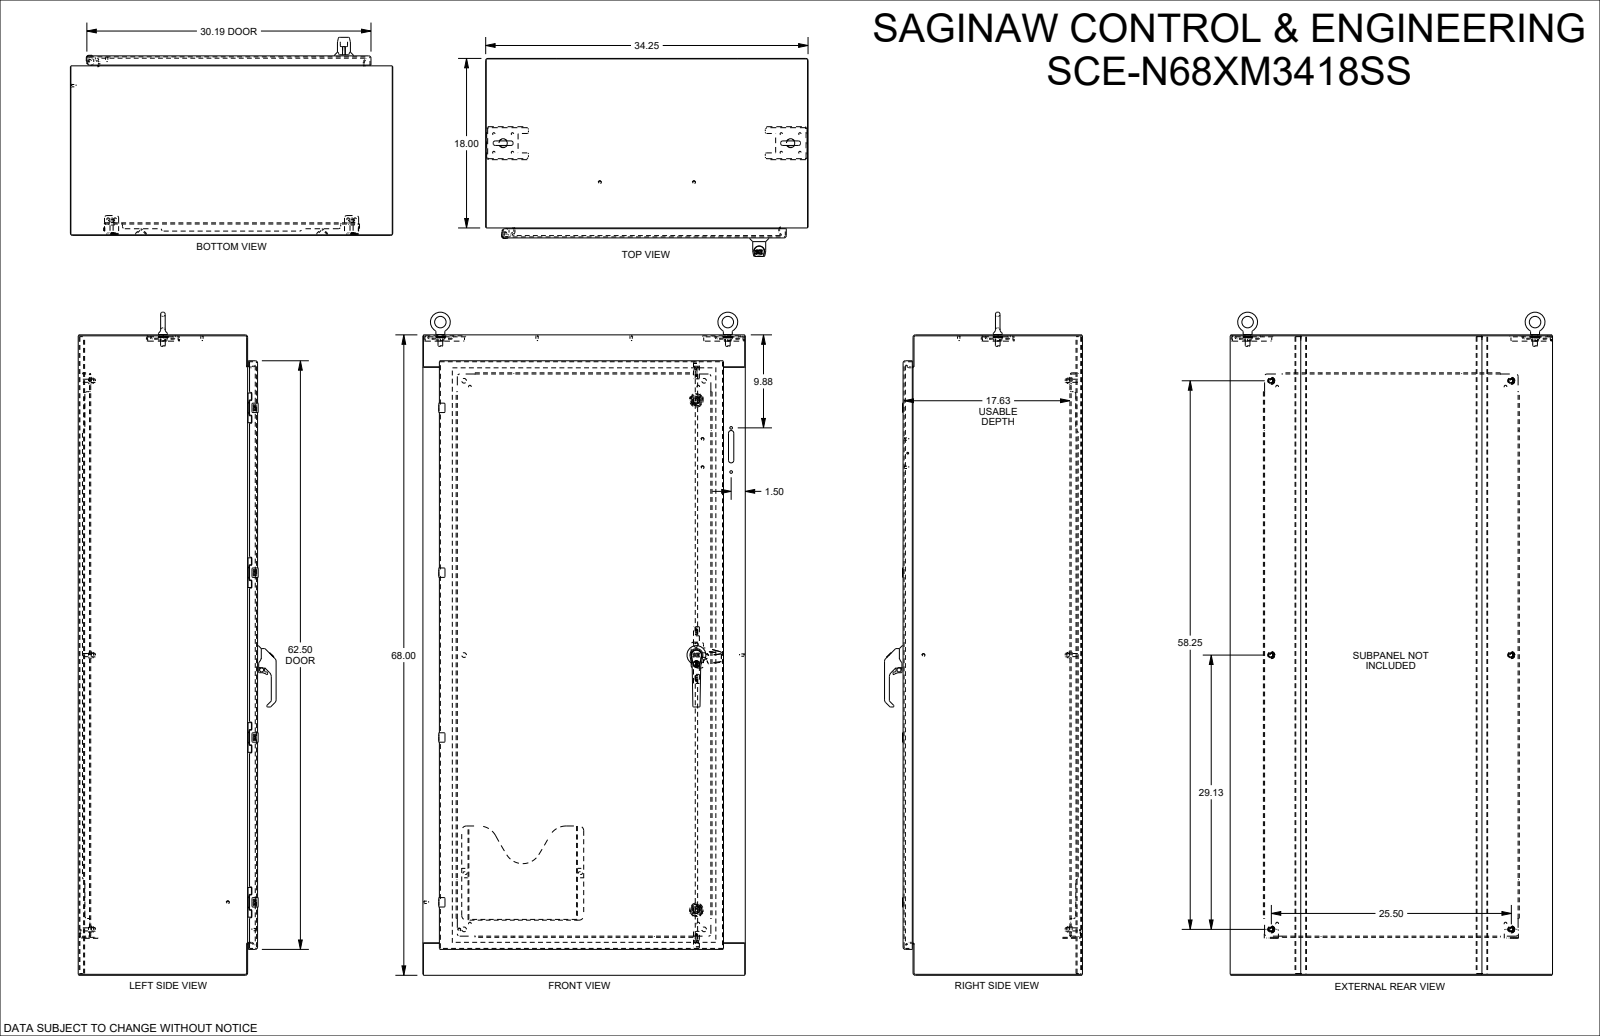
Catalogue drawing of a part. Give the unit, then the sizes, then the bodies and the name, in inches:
Units: inches
Overall size (bounding box): 70.945 × 34.25 × 21.046
Round holes (diameter × count): ⌀0.25 ×10, ⌀0.205 ×8, ⌀0.244 ×8, ⌀0.375 ×8, ⌀0.04 ×4, ⌀0.17 ×4, ⌀0.218 ×4, ⌀0.256 ×4, ⌀0.281 ×2, ⌀0.343 ×2, ⌀0.36 ×2, ⌀0.875 ×2
Round bosses / shafts (diameter × count): ⌀0.17 ×12, ⌀0.25 ×8, ⌀0.24 ×8, ⌀0.196 ×5, ⌀1.4 ×2, ⌀1.173 ×2, ⌀0.6 ×2, ⌀0.341 ×2
Partial cylindrical surfaces — rounded edges, fillets, slot ends (radius × count): R0.03 ×96, R0.015 ×68, R0.04 ×37, R0.062 ×32, R0.125 ×31, R0.02 ×24, R0.039 ×22, R0.079 ×21
Main face-to-face distances: 0.104, 18.954, 0.104, 34.146, 18.85, 19.058, 17.896, 1.058, 34.25, 67.896
Hole centre spacings: 17.5, 35, 0.493, 0.494, 0.984, 1.399, 1.4, 1.979
Volume: 960.6 in³ · Surface area: 18 356 in²
Bodies: 22 solids, 3144 faces (1331 planar, 1025 cylindrical, 788 other)
Part name (STEP PRODUCT): SCE-N68XM3418
STEP written by: SolidWorks 2023 (AUTOMOTIVE_DESIGN)
